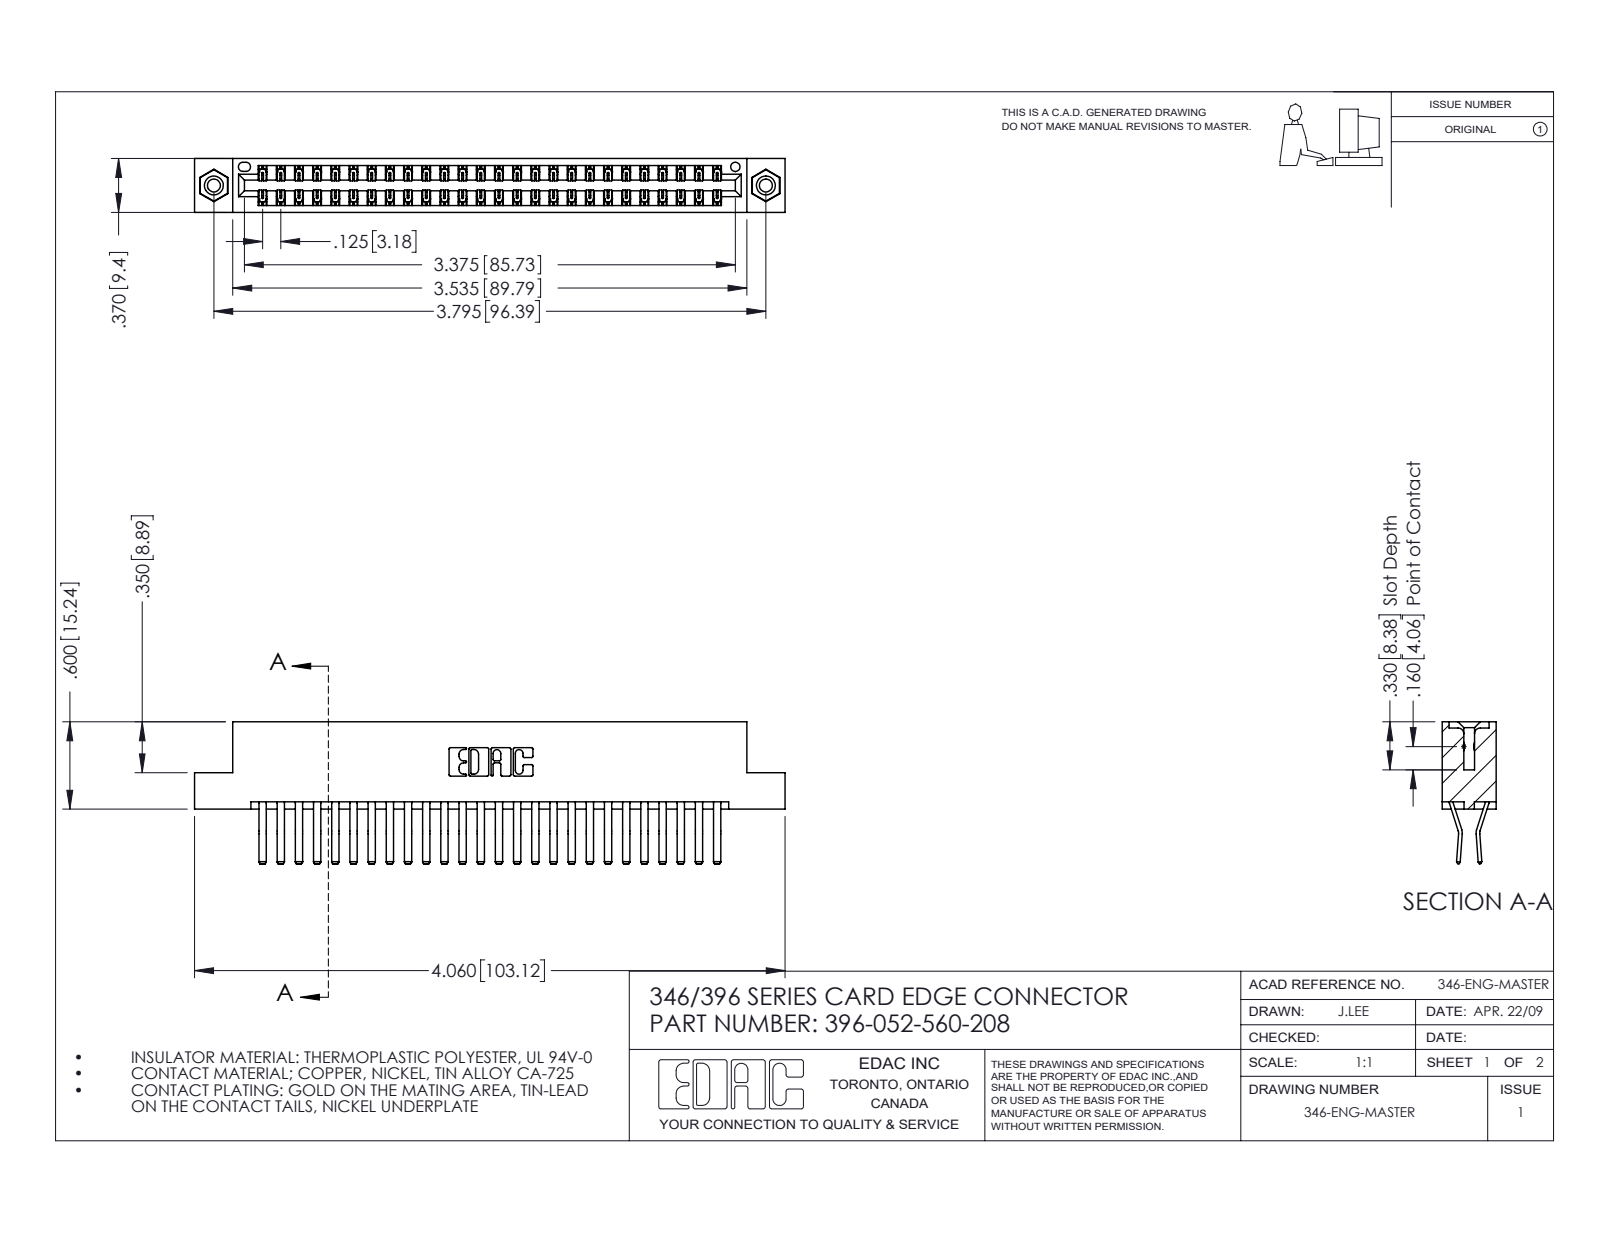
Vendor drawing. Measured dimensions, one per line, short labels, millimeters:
name: 346 Part_Flush Mounting Lugs - 0.156 Dia-TI; 345-250-001_345-250-003-102; 345-292-001_560 Tail; 396-052-560-208
written by: SolidWorks 2016 (CONFIG_CONTROL_DESIGN)
unit: mm
bodies: 55 solids, 2990 faces (1928 planar, 1046 cylindrical, 16 other)
size: 103.1 × 24.8 × 9.4
volume: 10 300 mm³; area: 14 790 mm²
holes: 2× ⌀2.3, 2× ⌀3.2, 2× ⌀4, 1× ⌀1.6
bosses: 2× ⌀3.9
rounds: 78× R0.2, 22× R0.3, 6× R0.2, 6× R0.8, 3× R0.7, 2× R0.3, 2× R0.4, 2× R0.6
face distances: 1.2, 8.2, 9.4, 6.4, 0.6, 1.8, 7.6, 7, 3.8, 5.6
hole spacings: 6.2, 91.1, 96.4
